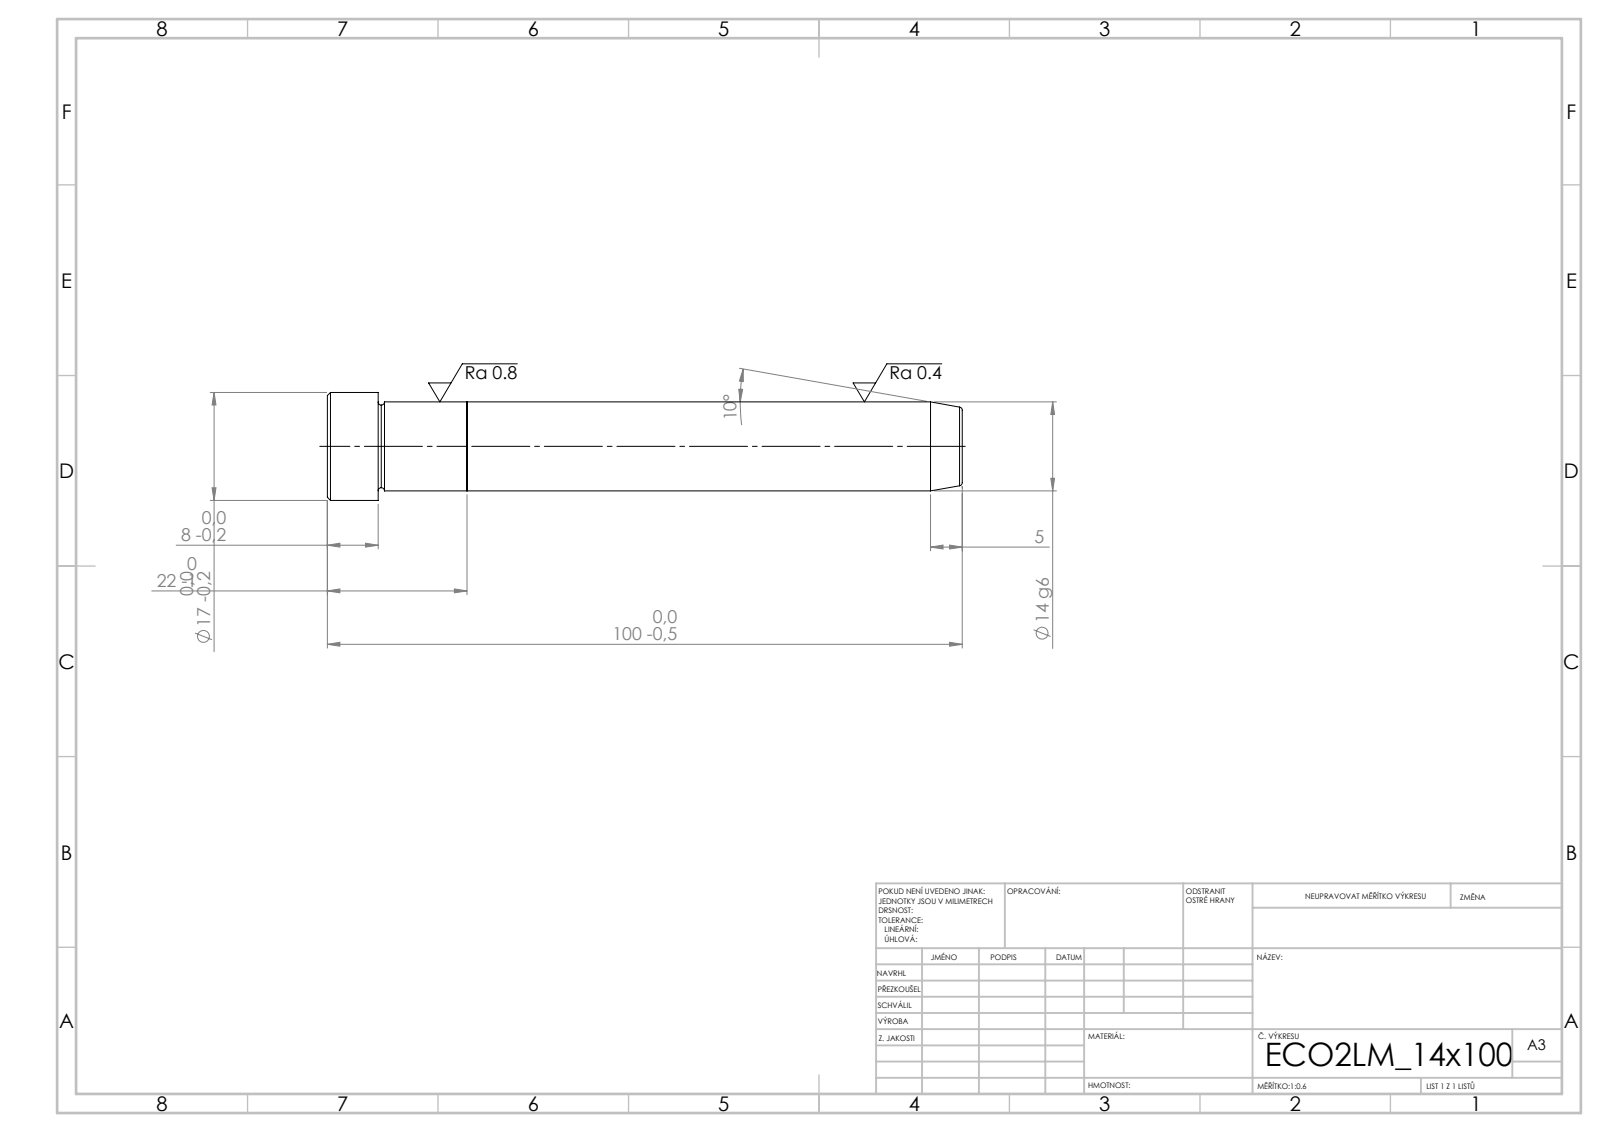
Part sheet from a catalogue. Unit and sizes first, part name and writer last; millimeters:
Units: millimetres
Overall size (bounding box): 100 × 17 × 17
Round bosses / shafts (diameter × count): ⌀17 ×1, ⌀14 ×1
Main face-to-face distances: 22, 78, 100, 92, 14, 8
Volume: 15 861 mm³ · Surface area: 5 189 mm²
Bodies: 2 solids, 21 faces (5 planar, 6 cylindrical, 10 other)
STEP written by: SolidWorks 2019 (CONFIG_CONTROL_DESIGN)
